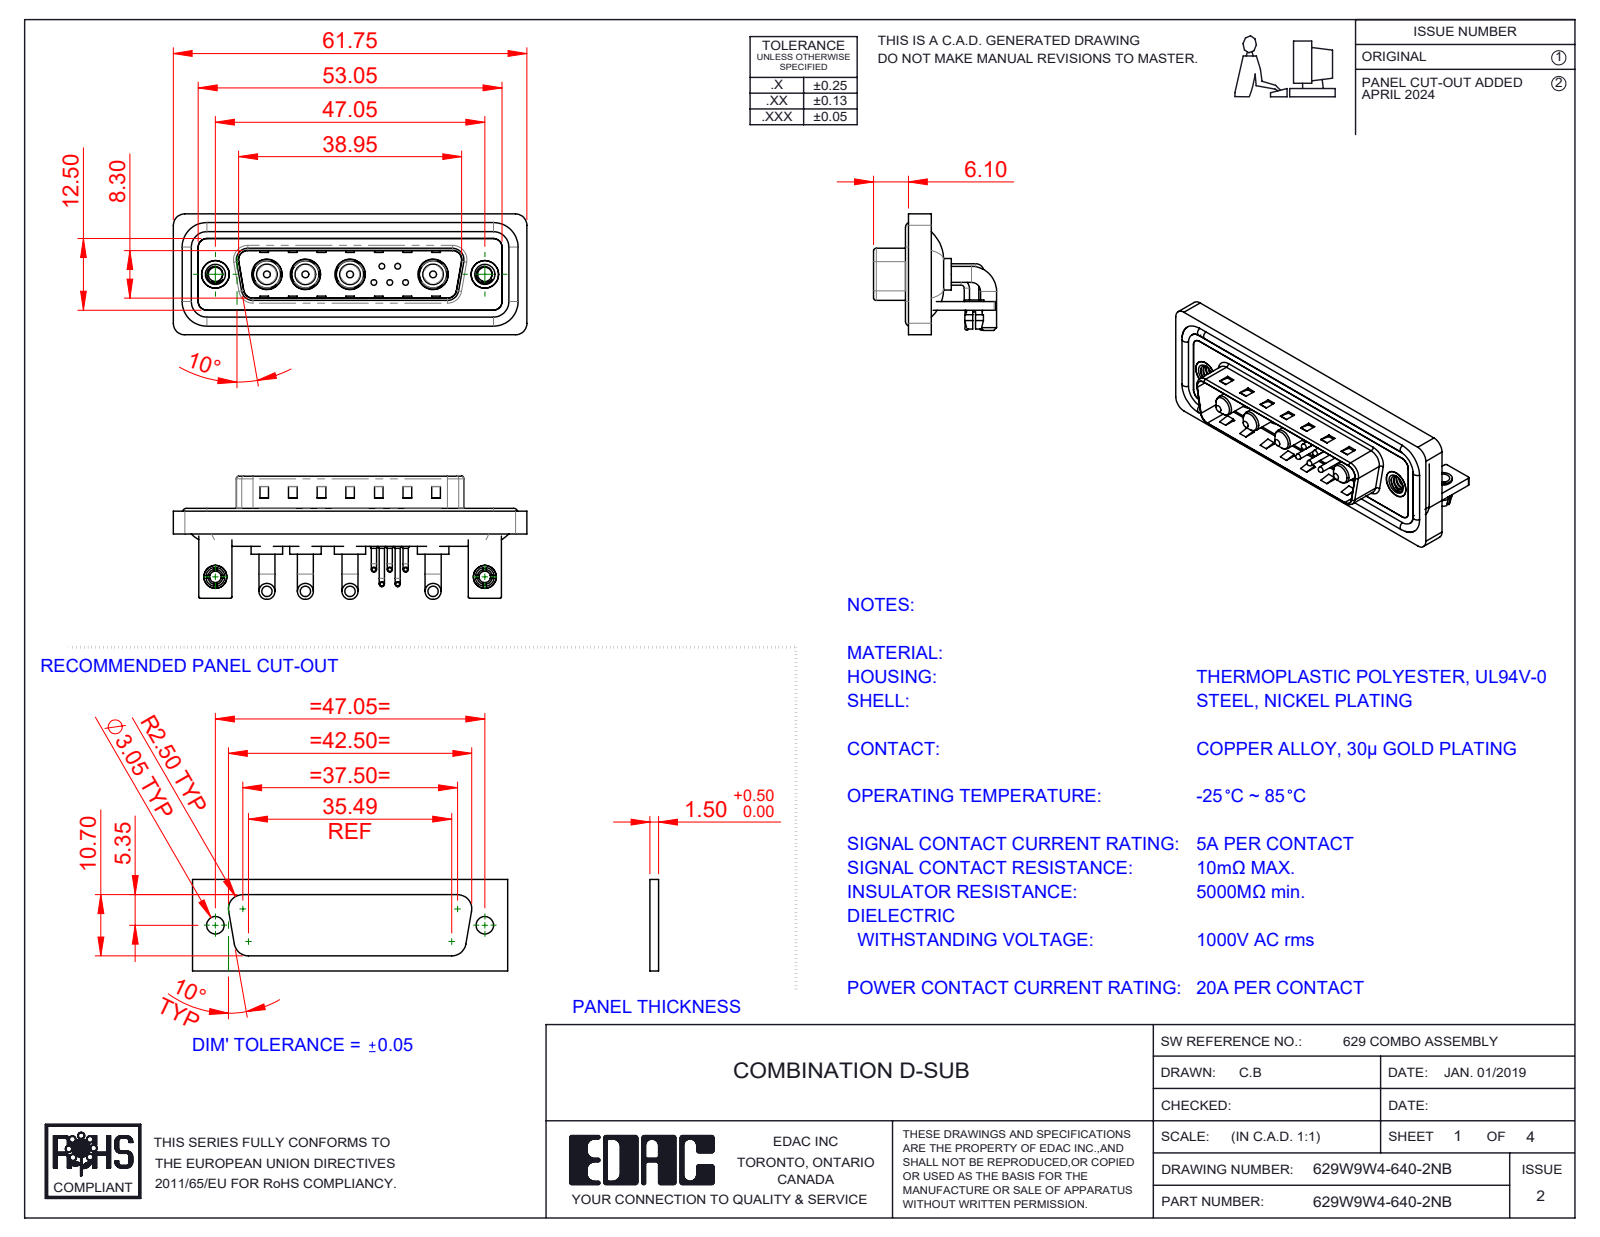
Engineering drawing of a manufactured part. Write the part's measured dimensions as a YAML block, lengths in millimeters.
part_name: "Power Pin_20A RA; 629Combo Shell Rear_25 Contacts; 629Combo Contact Row 1; 629Combo Housing_9W4 (+7 more)"
step_written_by: "SolidWorks 2023 (CONFIG_CONTROL_DESIGN)"
units: millimeters
bodies: {solids: 24, faces: 1335, planar: 637, cylindrical: 502, other: 196}
overall_size: [61.75, 21.5, 21.1]
volume: 8012
surface_area: 13175
round_holes:
  - {diameter: 2, count: 7}
  - {diameter: 0.75, count: 5}
  - {diameter: 1.6, count: 5}
  - {diameter: 2.5, count: 4}
  - {diameter: 4.85, count: 4}
  - {diameter: 5.3, count: 4}
  - {diameter: 3.2, count: 2}
  - {diameter: 4, count: 2}
  - {diameter: 4.8, count: 2}
  - {diameter: 5, count: 2}
round_bosses_or_shafts:
  - {diameter: 0.9, count: 10}
  - {diameter: 2.8, count: 8}
  - {diameter: 1.5, count: 5}
  - {diameter: 1, count: 5}
  - {diameter: 0.65, count: 5}
  - {diameter: 5.5, count: 4}
  - {diameter: 5.2, count: 4}
  - {diameter: 4.75, count: 4}
partial_cylinders:
  - {radius: 2, count: 19}
  - {radius: 1.5, count: 18}
  - {radius: 0.25, count: 16}
  - {radius: 0.5, count: 9}
  - {radius: 1.6, count: 8}
  - {radius: 1.01, count: 5}
  - {radius: 0.6, count: 4}
  - {radius: 0.65, count: 4}
face_to_face_distances: [0.4, 1.5, 0.8, 2.9, 2.1, 1.1, 3.7, 4.1, 4.5, 1.6]
hole_center_spacings: [3.16, 2.77, 5.04, 14.5, 47.05, 2.78, 4.4, 4.41]
